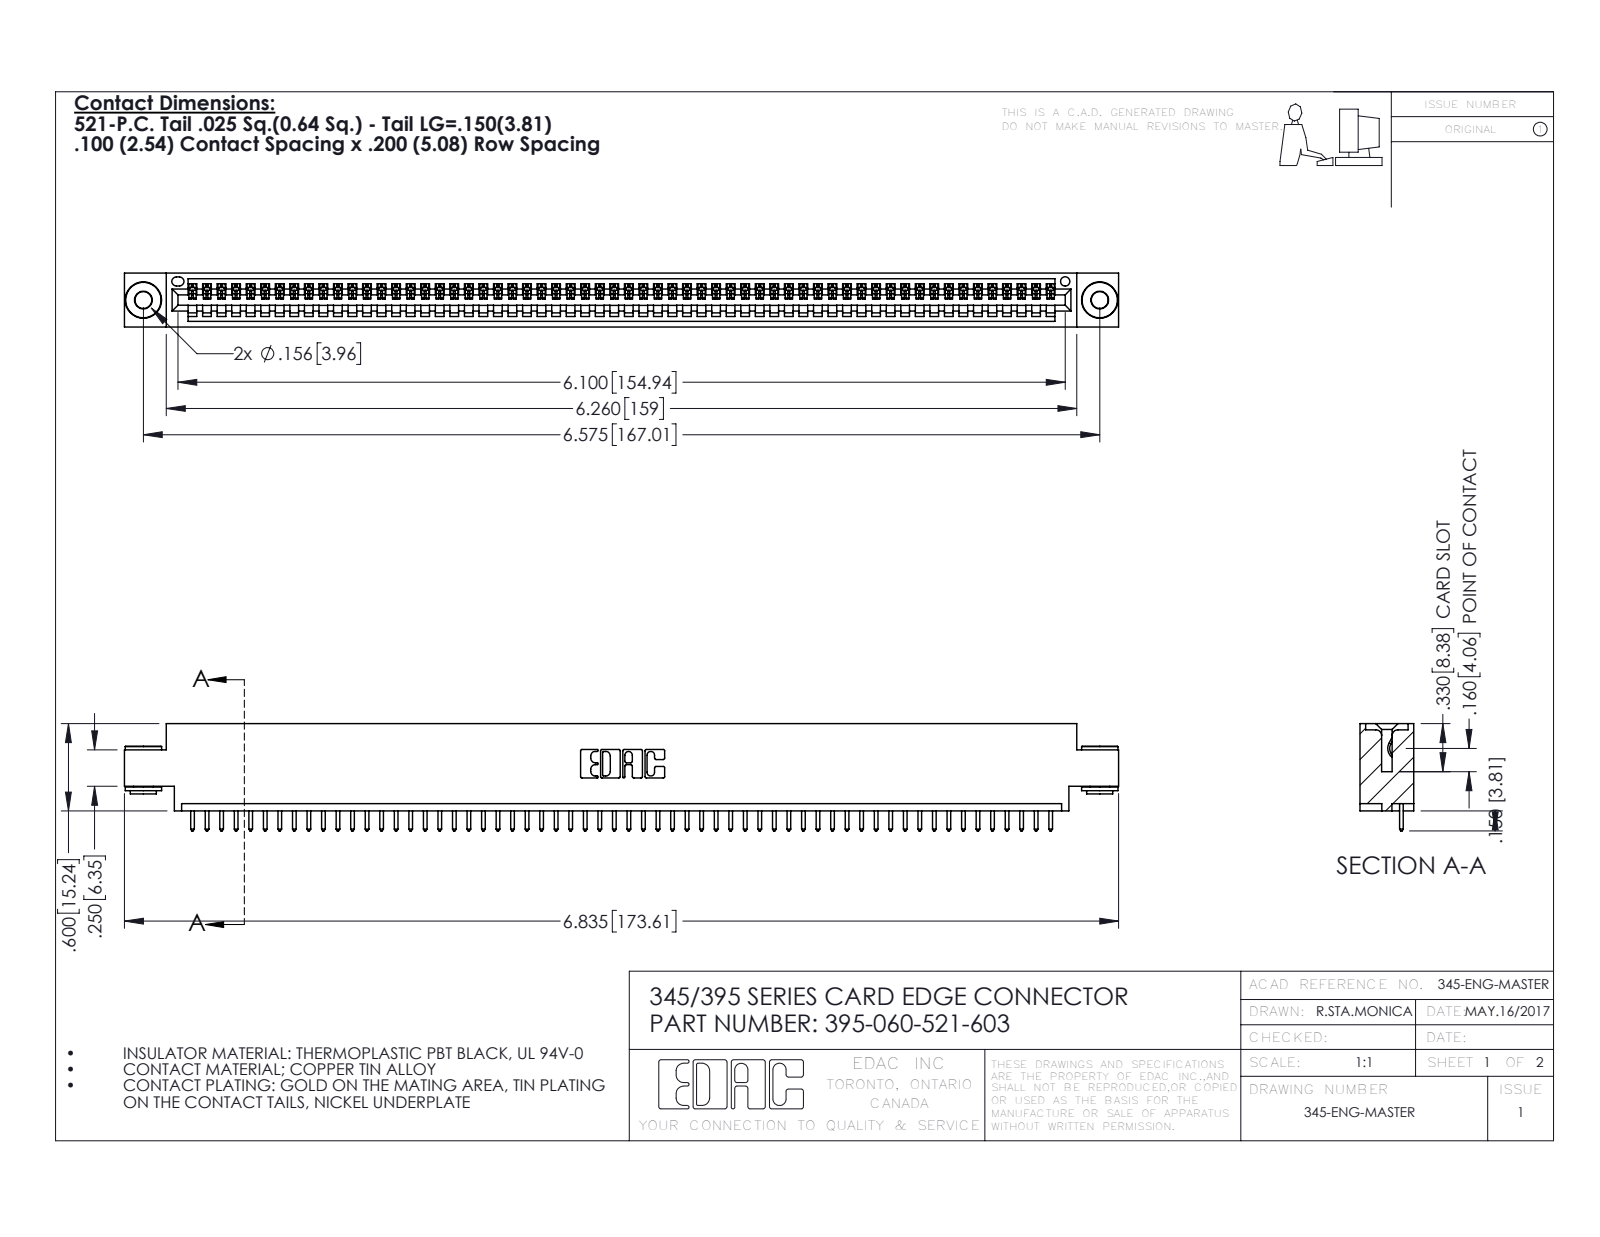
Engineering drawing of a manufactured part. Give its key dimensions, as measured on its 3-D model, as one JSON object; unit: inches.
{"part_name": "345-250-002_345-250-002-102; 345-292-001_345-293-121; 395-060-521-603; 345 Part_0.170 Offset - 0.156 Dia-TH", "step_written_by": "SolidWorks 2016 (CONFIG_CONTROL_DESIGN)", "units": "inches", "bodies": {"solids": 63, "faces": 3648, "planar": 2494, "cylindrical": 1146, "other": 8}, "overall_size": [6.835, 0.737, 0.37], "volume_in3": 0.999, "surface_area_in2": 33.6, "round_holes": [[0.116, 2], [0.156, 2], [0.064, 1]], "round_bosses_or_shafts": [[0.25, 2], [0.18, 2], [0.136, 2]], "partial_cylinders_radius": [[0.006, 120], [0.01, 120], [0.01, 22], [0.007, 6], [0.031, 6], [0.026, 3], [0.031, 2], [0.04, 2]], "face_to_face_distances": [0.072, 0.298, 0.37, 0.2, 0.098, 0.272, 0.025, 0.225, 0.175, 0.149], "hole_center_spacings": [0.27, 6.339, 6.575]}
